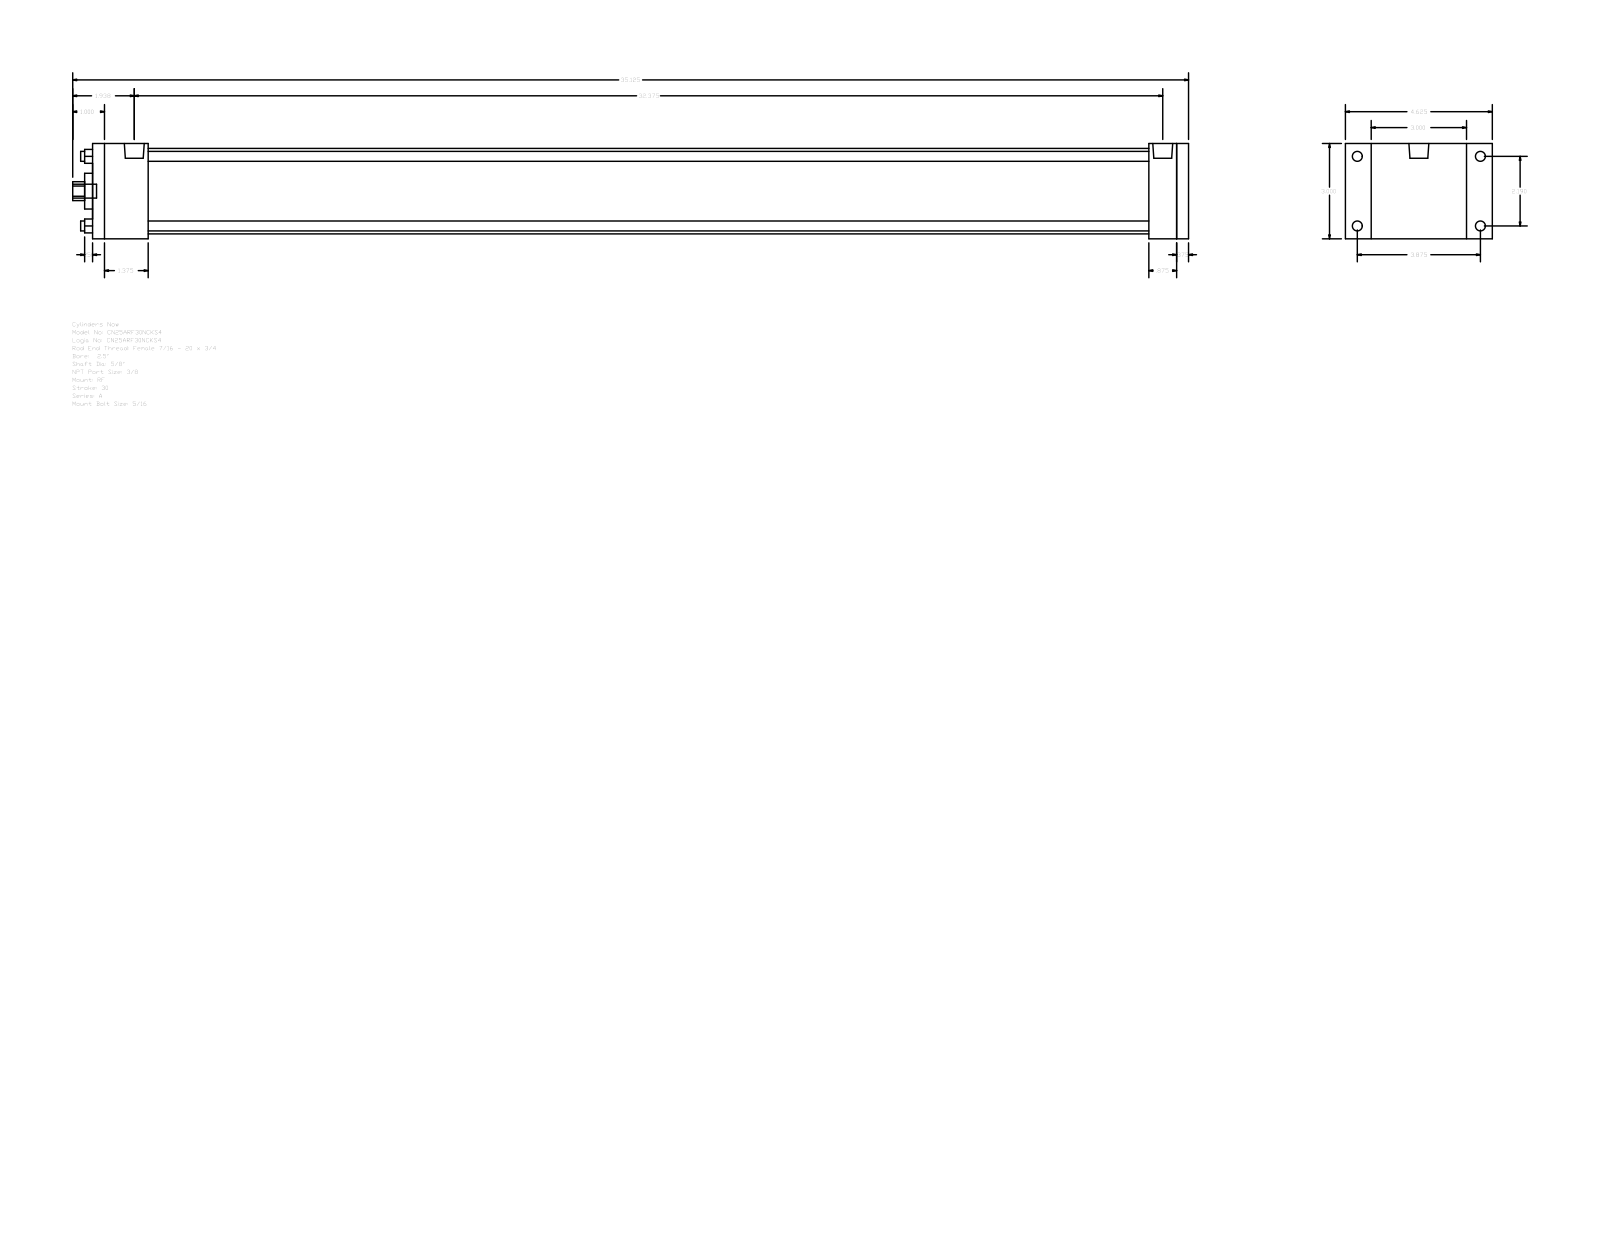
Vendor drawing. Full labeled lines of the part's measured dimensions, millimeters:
Part name (STEP PRODUCT): A_RF__0250_0.625
STEP written by: GSSL Pune (CONFIG_CONTROL_DESIGN)
Units: millimetres
Bodies: 0 solids, 92 faces (64 planar, 28 cylindrical, 0 other)
Overall size (bounding box): 892.17 × 117.47 × 76.2
Round holes (diameter × count): ⌀7.94 ×4, ⌀15.88 ×1, ⌀28.57 ×1, ⌀68.33 ×1
Round bosses / shafts (diameter × count): ⌀7.94 ×4, ⌀5.56 ×4, ⌀15.93 ×2, ⌀11.11 ×1
Partial cylindrical surfaces — rounded edges, fillets, slot ends (radius × count): R7.54 ×1
Main face-to-face distances: 76.2, 876.29, 9.52, 866.77, 44.45, 31.75, 844.54, 800.09, 822.32, 831.84
Hole centre spacings: 39.33, 55.62, 78.66
